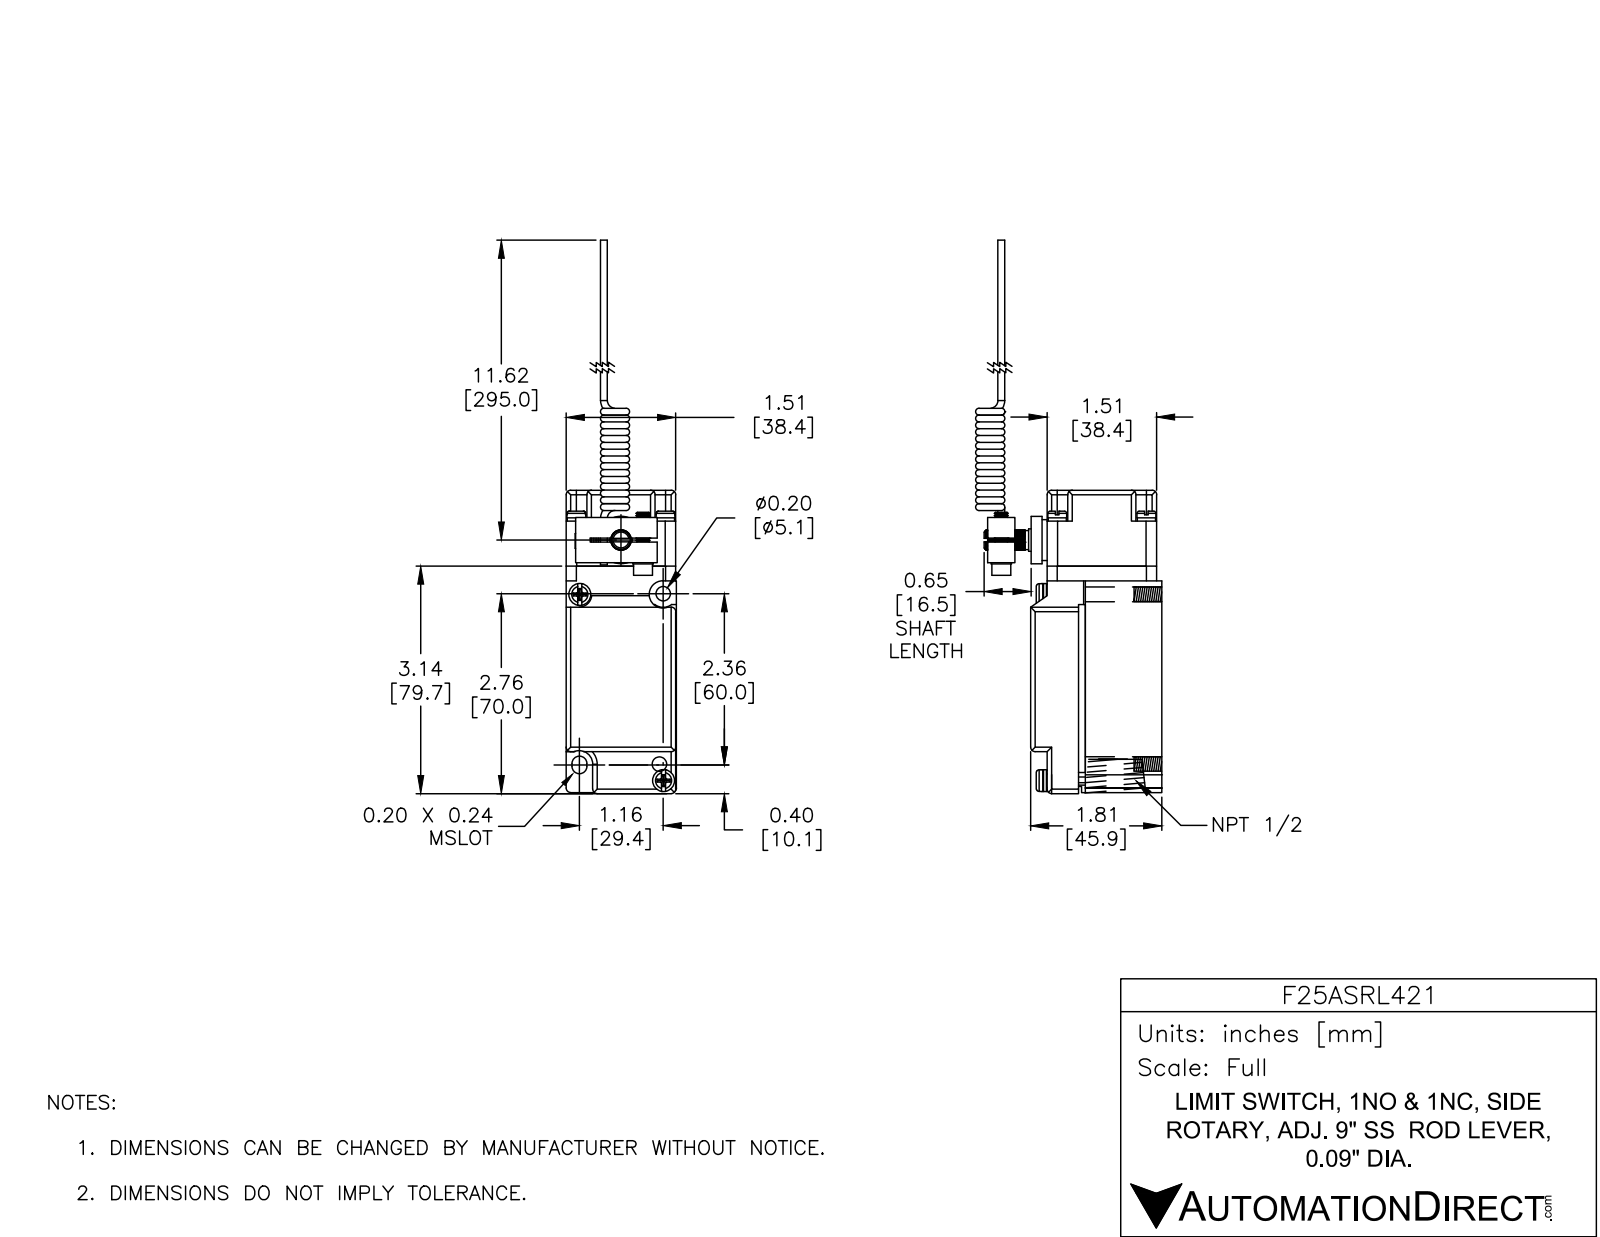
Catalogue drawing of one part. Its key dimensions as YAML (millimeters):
part_name: "F25ASRL421"
step_written_by: "SolidWorks 2018 (AUTOMOTIVE_DESIGN)"
units: millimeters
bodies: {solids: 31, faces: 761, planar: 440, cylindrical: 155, other: 166}
overall_size: [383.8, 65.2, 38.6]
volume: 171600
surface_area: 50720
round_holes:
  - {diameter: 4.5, count: 4}
  - {diameter: 4.8, count: 3}
  - {diameter: 5.1, count: 3}
  - {diameter: 3.4, count: 1}
  - {diameter: 5.2, count: 1}
  - {diameter: 5.3, count: 1}
  - {diameter: 7.2, count: 1}
  - {diameter: 14.7, count: 1}
round_bosses_or_shafts:
  - {diameter: 6.6, count: 4}
  - {diameter: 6.4, count: 4}
  - {diameter: 7.7, count: 2}
  - {diameter: 7.6, count: 2}
  - {diameter: 16.6, count: 1}
  - {diameter: 14.4, count: 1}
  - {diameter: 7.8, count: 1}
  - {diameter: 7.1, count: 1}
partial_cylinders:
  - {radius: 1.6, count: 29}
  - {radius: 0.8, count: 16}
  - {radius: 0.4, count: 8}
  - {radius: 3.7, count: 8}
  - {radius: 3.6, count: 4}
  - {radius: 2.6, count: 2}
  - {radius: 4.8, count: 2}
  - {radius: 4.8, count: 2}
face_to_face_distances: [2.4, 29.2, 26.8, 38.6, 16.8, 19.2, 45.9, 38.4, 5.8, 11]
hole_center_spacings: [31.2, 31.2, 44.2, 71.5, 5.7, 6, 14.2, 21.1]
